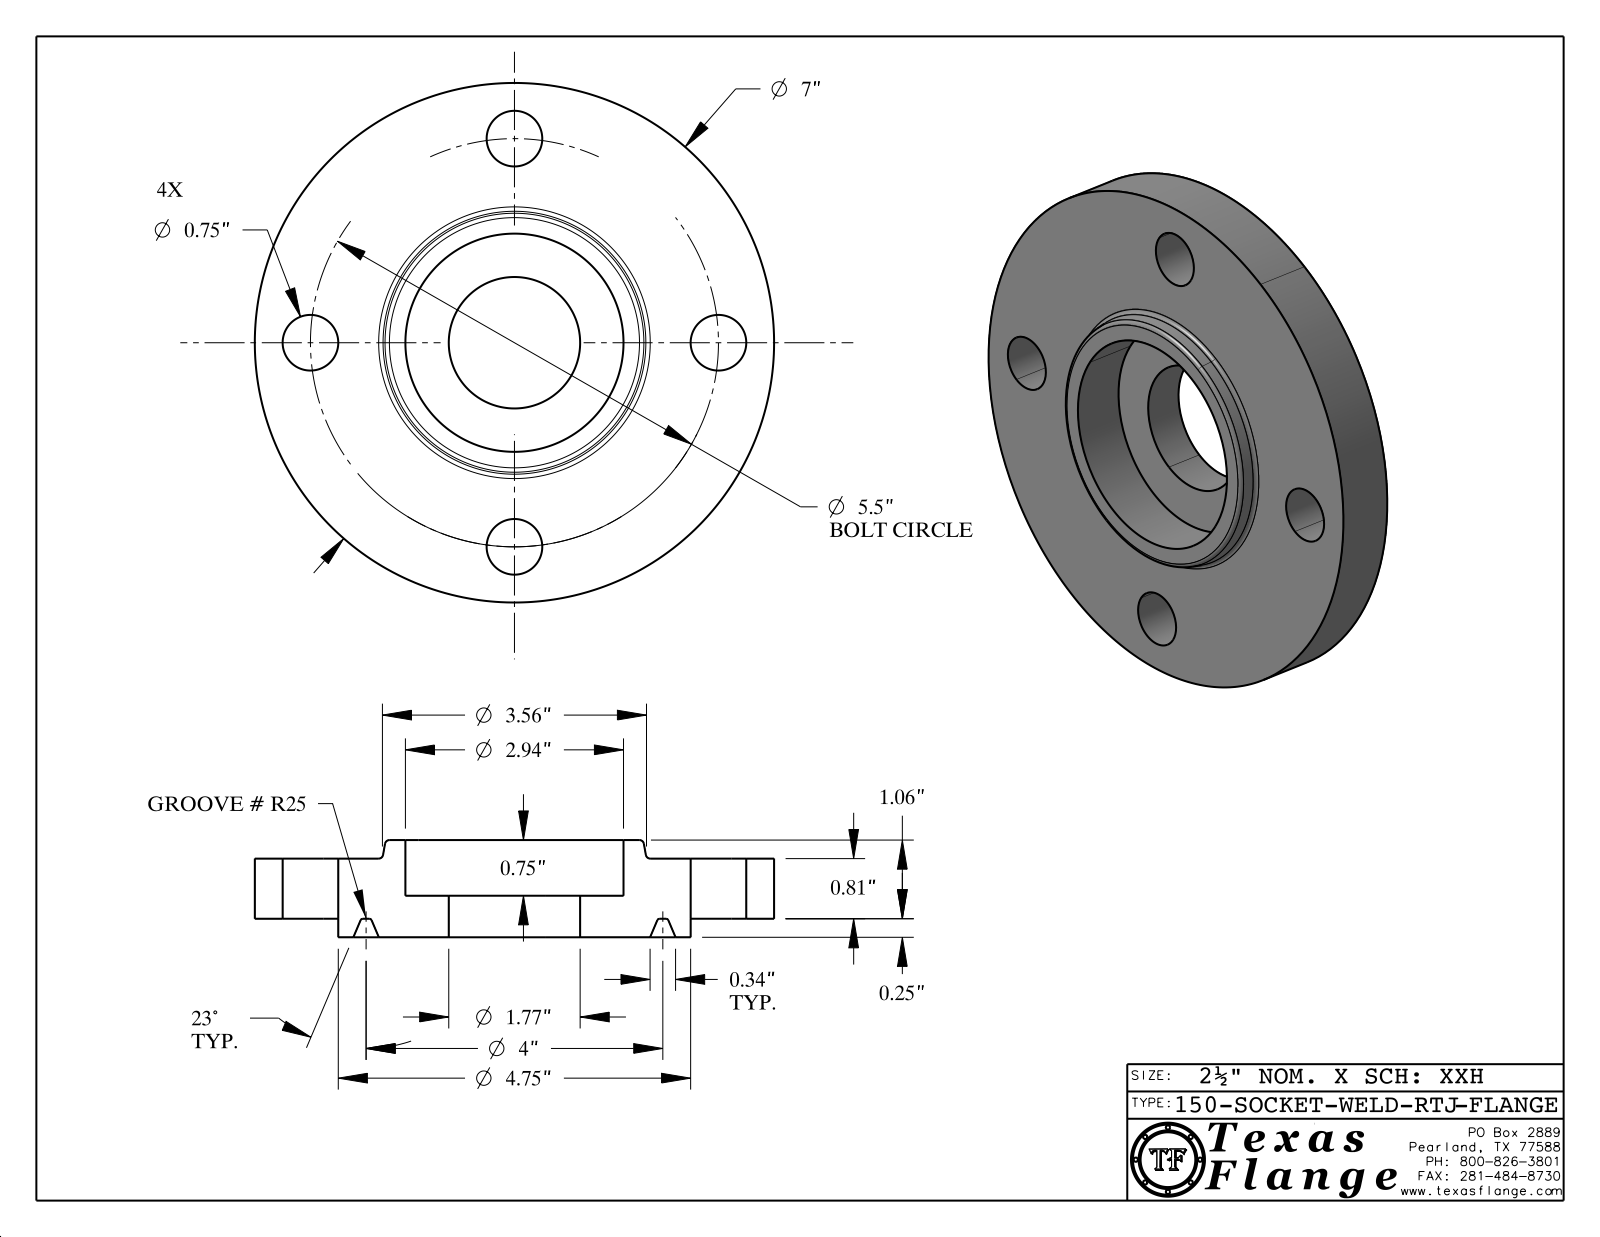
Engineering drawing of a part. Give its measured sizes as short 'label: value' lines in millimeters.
name: 150-SOCKET-WELD-RTJ
written by: CATIA V5 STEP AP214 (AUTOMOTIVE_DESIGN)
unit: mm
bodies: 1 solid, 422 faces (372 planar, 36 cylindrical, 14 other)
size: 177.8 × 177.8 × 33.3
volume: 481 500 mm³; area: 73 420 mm²
holes: 4× ⌀19.1, 1× ⌀12.6, 1× ⌀45, 1× ⌀74.7
bosses: 8× ⌀0.8, 1× ⌀177.8, 1× ⌀120.7, 1× ⌀9.9
face distances: 20.6, 6.4, 26.9, 14.2, 7.9, 12.7, 33.3, 19.1, 26.5, 20.2
hole spacings: 69.9, 98.8, 53.5, 129.1, 139.7
